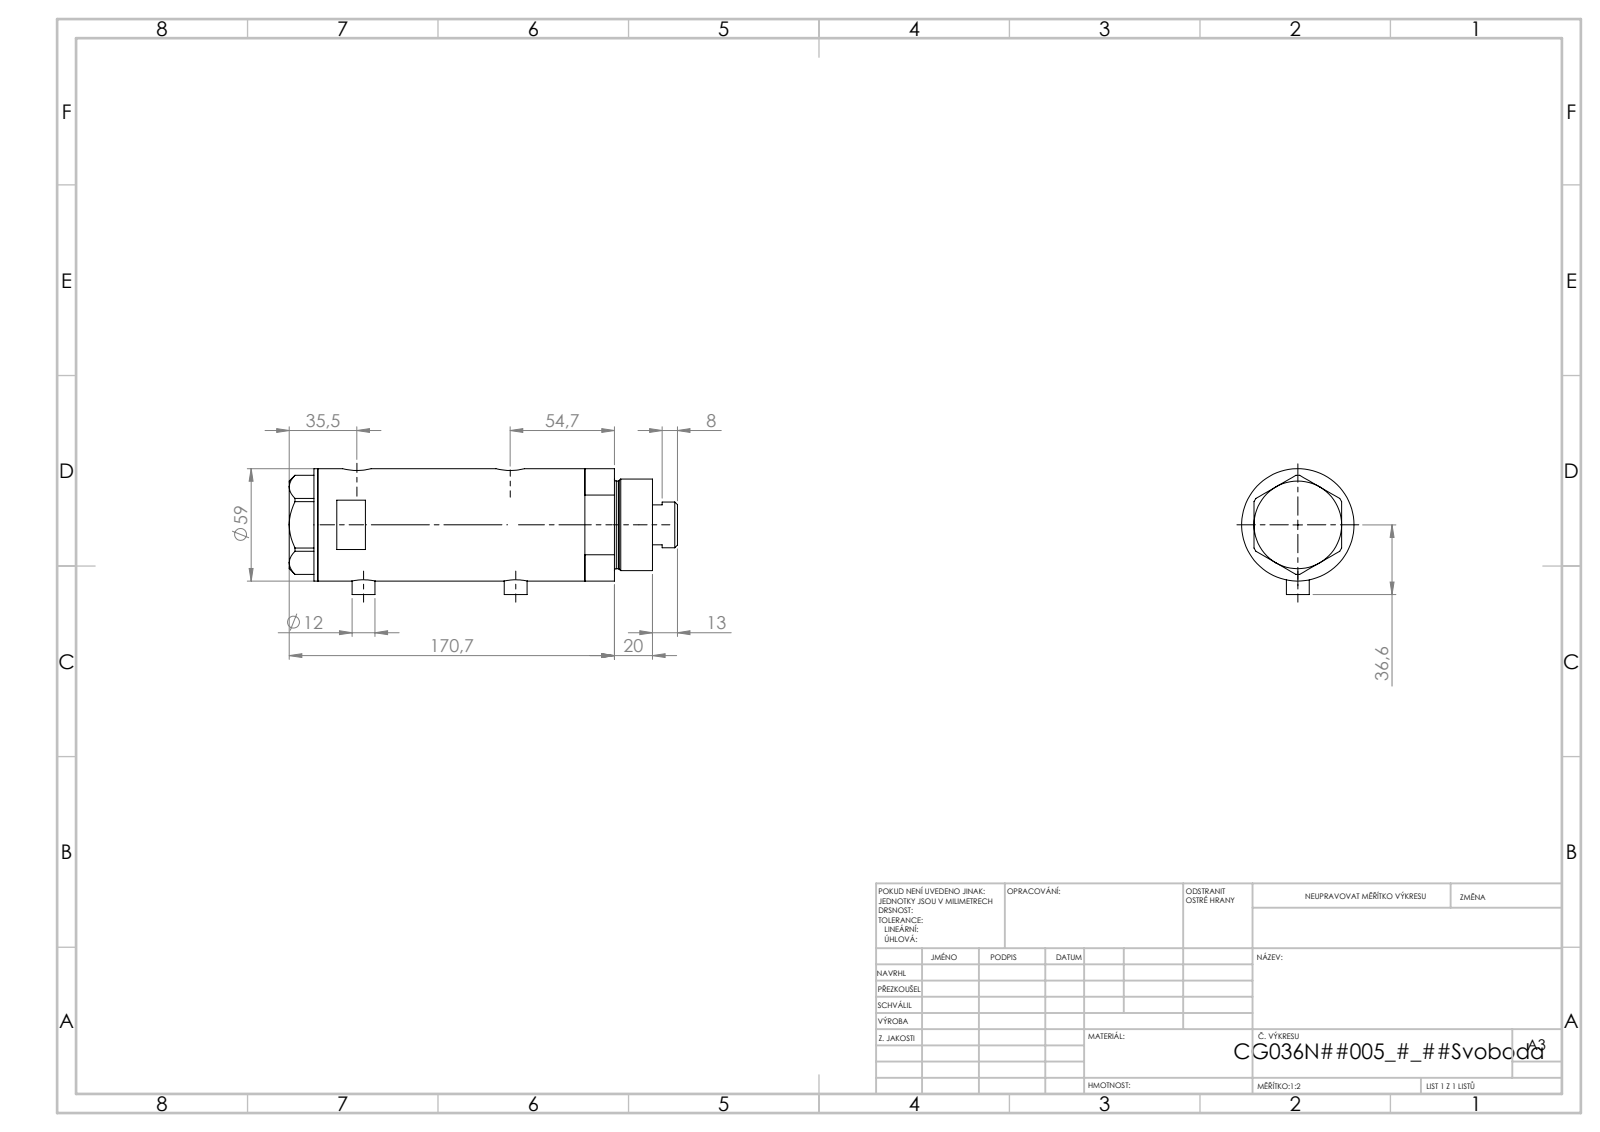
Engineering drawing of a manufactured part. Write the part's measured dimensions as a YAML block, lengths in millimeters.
part_name: "V270CG_BACK; V270CG_VC; V270CG_MIDDLE; V270CG_FRONT"
step_written_by: "SolidWorks 2019 (CONFIG_CONTROL_DESIGN)"
units: millimeters
bodies: {solids: 4, faces: 126, planar: 53, cylindrical: 53, other: 20}
overall_size: [203.8, 66.1, 59]
volume: 485662
surface_area: 99813
round_holes:
  - {diameter: 5, count: 2}
  - {diameter: 9.73, count: 2}
  - {diameter: 12.5, count: 2}
  - {diameter: 15, count: 2}
  - {diameter: 8.5, count: 1}
  - {diameter: 25, count: 1}
  - {diameter: 26.5, count: 1}
  - {diameter: 36, count: 1}
  - {diameter: 40, count: 1}
  - {diameter: 52, count: 1}
round_bosses_or_shafts:
  - {diameter: 12, count: 2}
  - {diameter: 59, count: 1}
  - {diameter: 48, count: 1}
  - {diameter: 46, count: 1}
  - {diameter: 24, count: 1}
face_to_face_distances: [102.2, 23.5, 78.7, 15, 38.5, 117.2, 2, 175.7, 190.7, 152.2]
hole_center_spacings: [2.9, 3.5, 77, 79.9, 80.5, 83.4]
